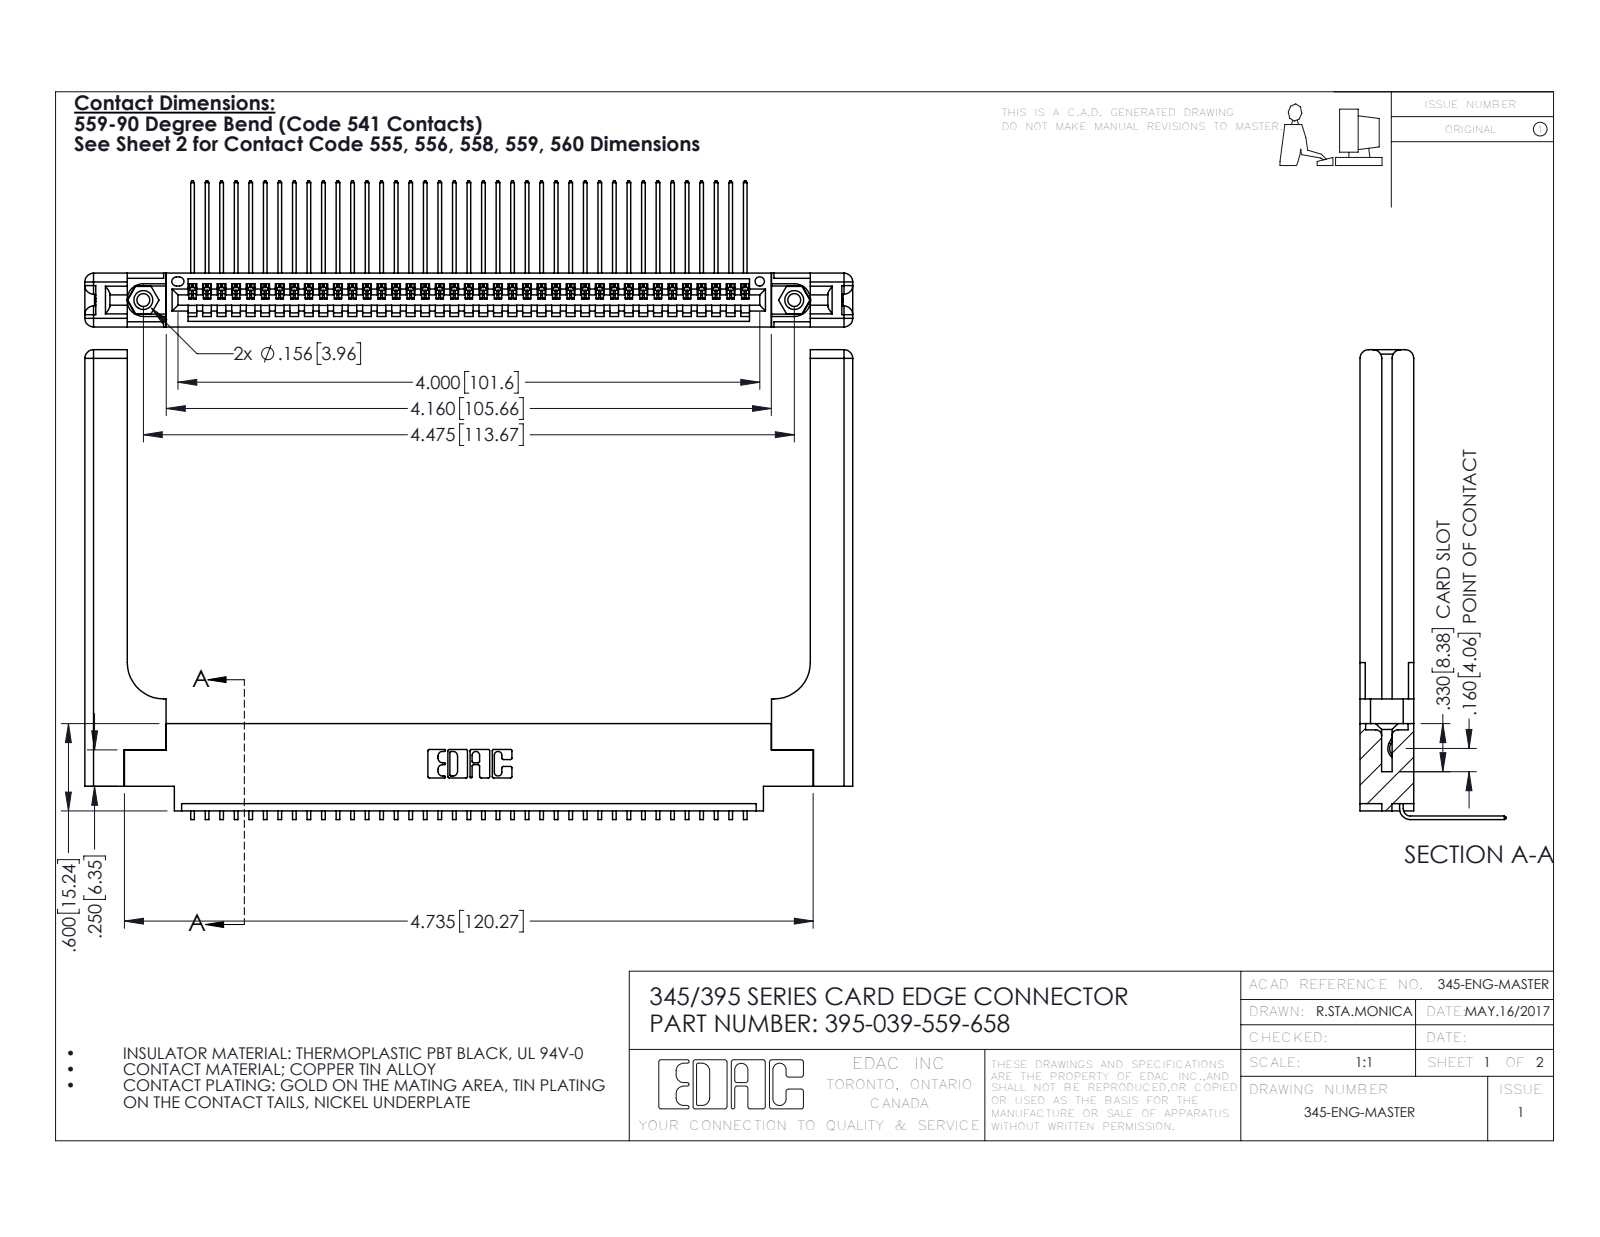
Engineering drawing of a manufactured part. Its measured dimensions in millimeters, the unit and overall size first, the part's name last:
Units: millimetres
Overall size (bounding box): 134.1 × 82 × 25.5
Round holes (diameter × count): ⌀2.3 ×2, ⌀3.2 ×2, ⌀4 ×2, ⌀1.6 ×1
Round bosses / shafts (diameter × count): ⌀3.9 ×2
Partial cylindrical surfaces — rounded edges, fillets, slot ends (radius × count): R0.2 ×78, R0.3 ×22, R1.5 ×16, R0.2 ×6, R0.8 ×6, R0.7 ×3, R0.8 ×2, R0.8 ×2
Main face-to-face distances: 9.4, 1.8, 7.6, 2.5, 6.9, 0.6, 5.1, 3.8, 3.8, 5.7
Hole centre spacings: 6.9, 107.7, 113.7
Volume: 21 240 mm³ · Surface area: 23 070 mm²
Bodies: 44 solids, 2726 faces (1870 planar, 796 cylindrical, 60 other)
Part name (STEP PRODUCT): 345-250-001_345-250-001-102; 345-220-058_345-220-058; 345 Part_0.170 Offset - 0.156 Dia-TH; 395-039-559-658 (+1 more)
STEP written by: SolidWorks 2016 (CONFIG_CONTROL_DESIGN)
